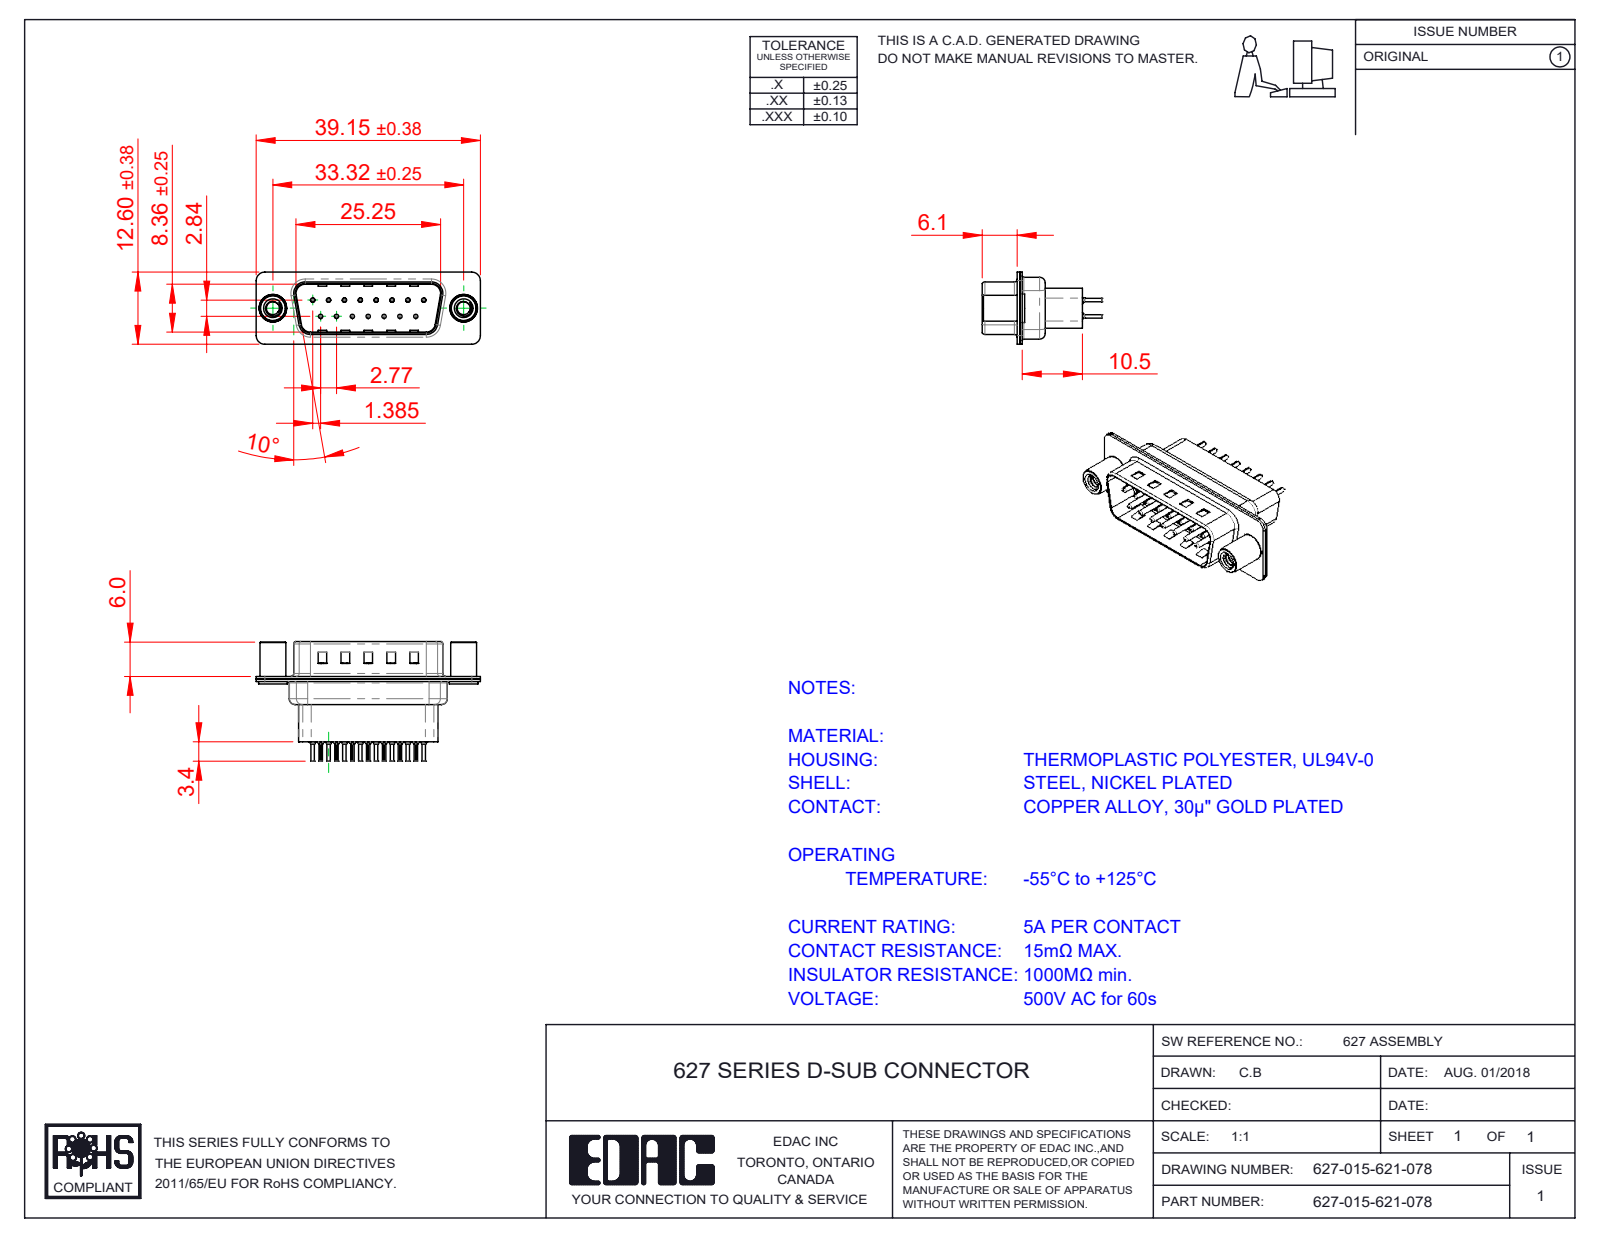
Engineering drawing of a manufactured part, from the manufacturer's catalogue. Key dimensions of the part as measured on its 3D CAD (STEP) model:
Part name (STEP PRODUCT): 627 Contact Row 1_21H; 627 Shell Rear_15 Contacts; 627 Shell Front_15 Contacts; 627 Contact Row 2_21H (+3 more)
STEP written by: SolidWorks 2020 (CONFIG_CONTROL_DESIGN)
Units: millimetres
Bodies: 20 solids, 1844 faces (501 planar, 716 cylindrical, 627 other)
Overall size (bounding box): 39.15 × 20.8 × 12.6
Volume: 2 602 mm³ · Surface area: 6 806 mm²
Round holes (diameter × count): ⌀0.2 ×15, ⌀0.35 ×15, ⌀1.1 ×15, ⌀1.6 ×15, ⌀2.26 ×2, ⌀4 ×2, ⌀4.8 ×2
Round bosses / shafts (diameter × count): ⌀2 ×15, ⌀1.5 ×15, ⌀0.75 ×15, ⌀0.6 ×15, ⌀5 ×2, ⌀4.9 ×2, ⌀4.5 ×2
Partial cylindrical surfaces — rounded edges, fillets, slot ends (radius × count): R0.1 ×30, R1.5 ×16, R2 ×12, R0.5 ×8, R1.6 ×8, R0.25 ×4, R0.6 ×4, R0.65 ×4
Main face-to-face distances: 0.4, 0.45, 0.9, 0.82, 9.58, 1.5, 0.68, 7.68, 1.4, 1.08
Hole centre spacings: 3.16, 2.77, 5.54, 8.31, 11.08, 5.03, 5.04, 7.48
